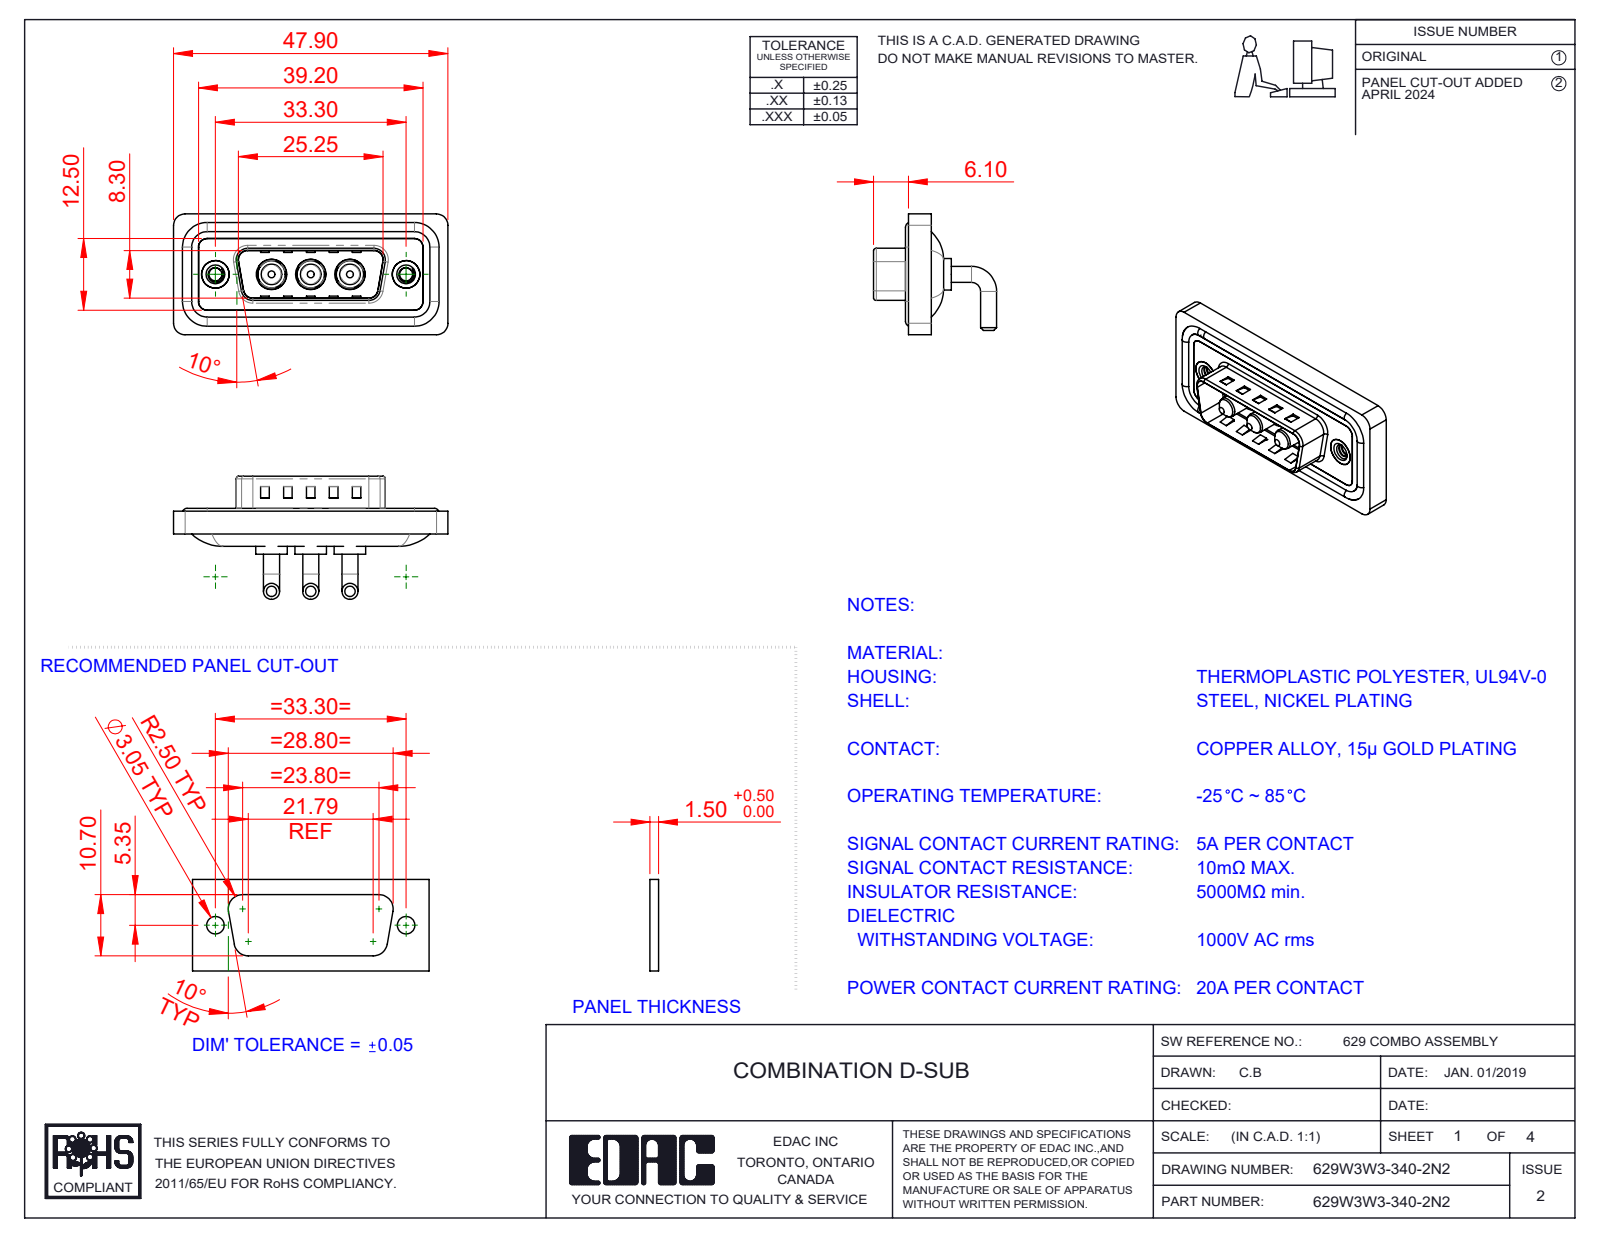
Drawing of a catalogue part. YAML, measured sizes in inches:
part_name: "629Combo Waterproof Housing_15 Contacts; 629Combo Shell Rear_15 Contacts; Power Pin_20A RA; 629Combo Shell Front_15 Contacts (+3 more)"
step_written_by: "SolidWorks 2023 (CONFIG_CONTROL_DESIGN)"
units: inches
bodies: {solids: 13, faces: 576, planar: 207, cylindrical: 247, other: 122}
overall_size: [1.886, 0.846, 0.831]
volume: 0.353
surface_area: 14.01
round_holes:
  - {diameter: 0.191, count: 3}
  - {diameter: 0.209, count: 3}
  - {diameter: 0.089, count: 2}
  - {diameter: 0.157, count: 2}
  - {diameter: 0.189, count: 2}
  - {diameter: 0.197, count: 2}
round_bosses_or_shafts:
  - {diameter: 0.11, count: 6}
  - {diameter: 0.063, count: 4}
  - {diameter: 0.217, count: 3}
  - {diameter: 0.205, count: 3}
  - {diameter: 0.187, count: 3}
  - {diameter: 0.148, count: 3}
  - {diameter: 0.142, count: 3}
  - {diameter: 0.193, count: 2}
partial_cylinders:
  - {radius: 0.079, count: 20}
  - {radius: 0.059, count: 18}
  - {radius: 0.02, count: 8}
  - {radius: 0.063, count: 8}
  - {radius: 0.01, count: 4}
  - {radius: 0.024, count: 4}
  - {radius: 0.026, count: 4}
  - {radius: 0.035, count: 4}
face_to_face_distances: [0.016, 0.114, 0.031, 0.043, 0.083, 0.063, 0.122, 0.098, 0.177, 0.146]
hole_center_spacings: [0.27, 0.386, 0.656, 0.925, 0.539, 1.311]
